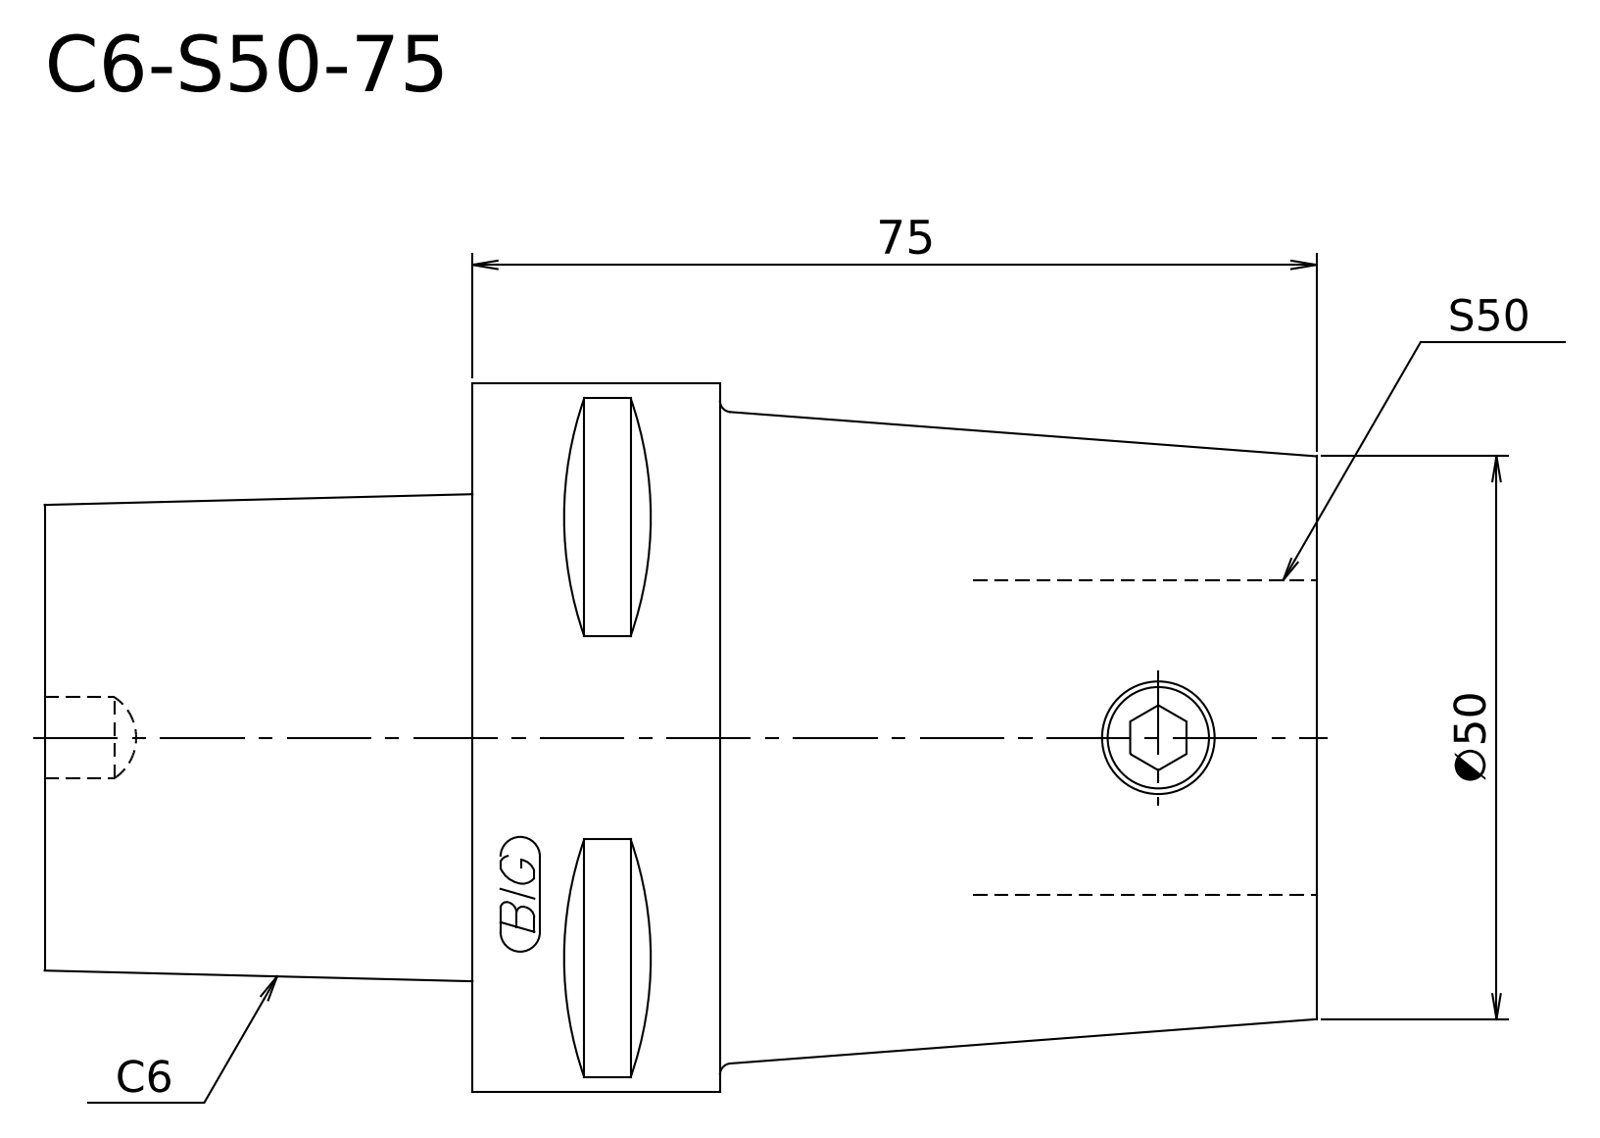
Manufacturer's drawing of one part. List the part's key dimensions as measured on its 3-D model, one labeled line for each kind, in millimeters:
Part name (STEP PRODUCT): C6-S50-75
STEP written by: SolidWorks 2021 (CONFIG_CONTROL_DESIGN)
Units: millimetres
Bodies: 1 solid, 12 faces (4 planar, 2 cylindrical, 6 other)
Overall size (bounding box): 113 × 63 × 63
Volume: 243 655 mm³ · Surface area: 23 788 mm²
Round bosses / shafts (diameter × count): ⌀63 ×1
Main face-to-face distances: 75, 38, 113, 60, 22, 53
